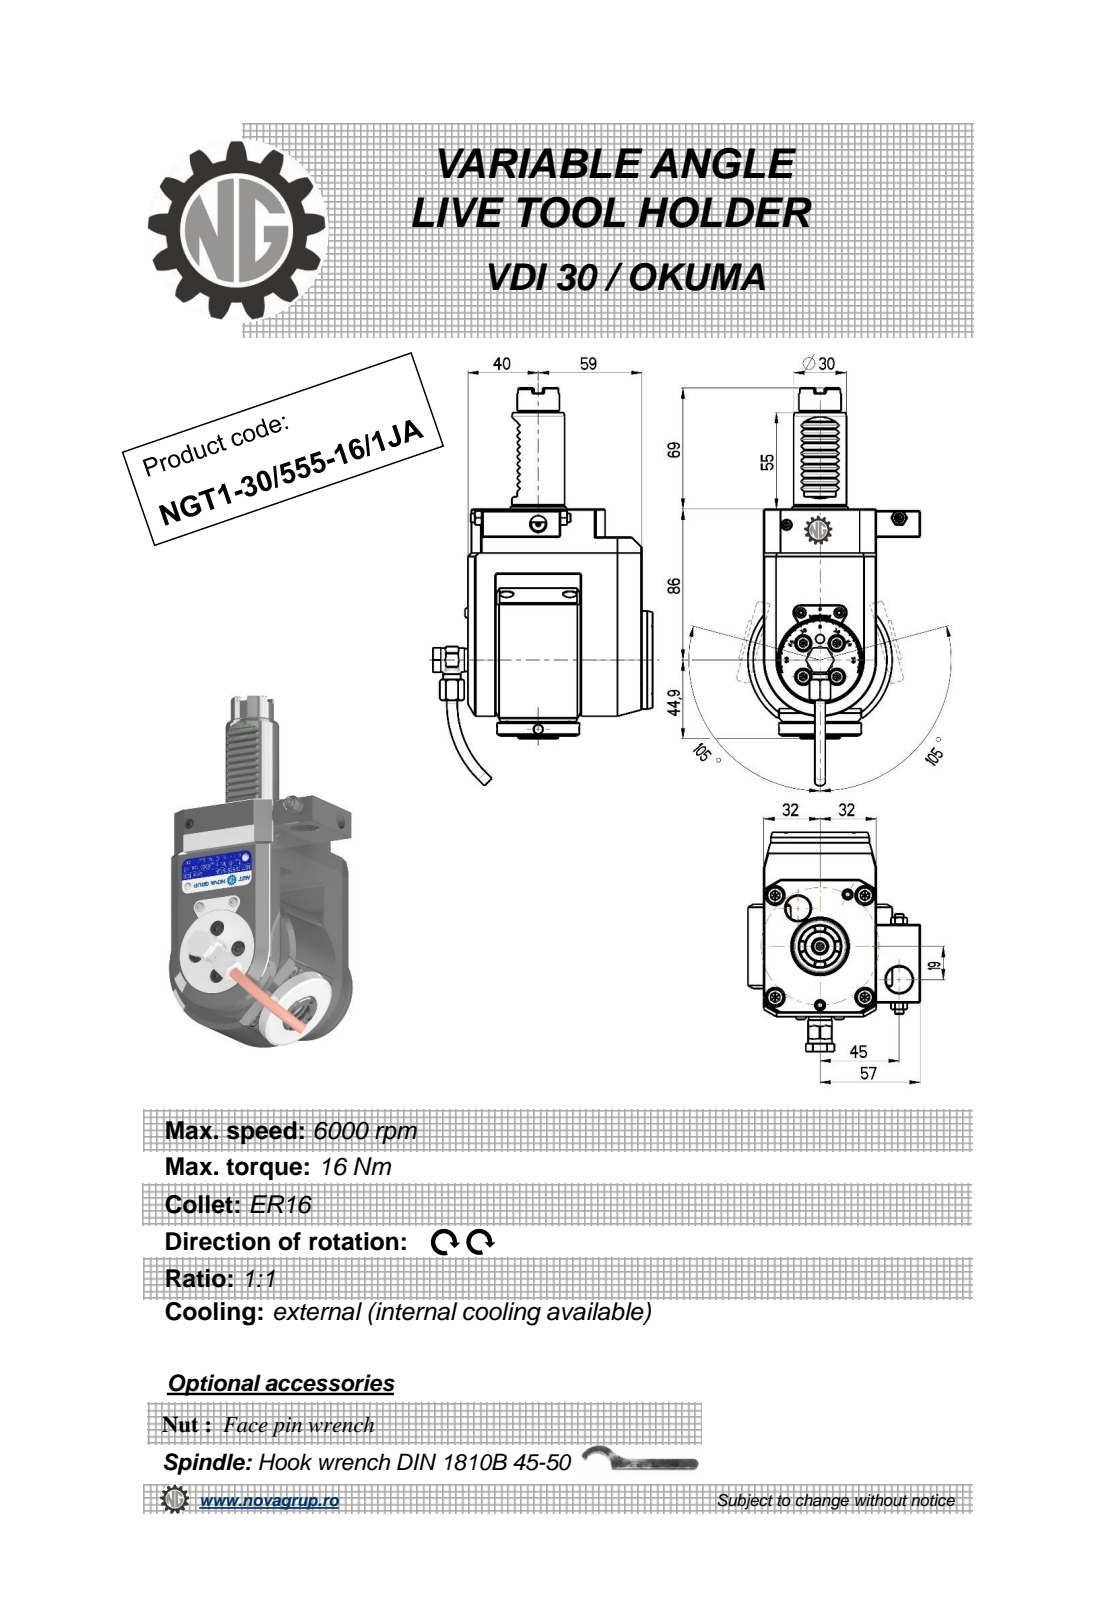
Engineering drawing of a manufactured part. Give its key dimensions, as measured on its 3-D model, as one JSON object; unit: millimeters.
{"part_name": "NGT1_30_555_16_1JA", "step_written_by": "PRO/ENGINEER BY PARAMETRIC TECHNOLOGY CORPORATION, 2010280 (CONFIG_CONTROL_DESIGN)", "units": "millimeters", "bodies": {"solids": 1, "faces": 568, "planar": 236, "cylindrical": 146, "other": 186}, "overall_size": [226.67, 124.9, 98], "volume_mm3": 771443, "surface_area_mm2": 75579, "round_holes": [[3.2, 4], [4, 3], [5, 2], [3, 1], [4.2, 1], [6, 1], [6.2, 1], [9, 1], [9.5, 1], [11, 1], [12.5, 1], [15, 1]], "round_bosses_or_shafts": [[10, 2], [6, 2], [5.7, 2], [82, 1], [56, 1], [47, 1], [36, 1], [30, 1]], "partial_cylinders_radius": [[0.26, 12], [0.3, 10], [0.16, 6], [0.5, 4], [1, 2], [7.7, 1], [32, 1]], "face_to_face_distances": [64, 16, 37, 6, 21, 89, 99, 105, 14, 41], "hole_center_spacings": [9.25, 13.08, 18.5, 49.87, 50.26, 0.4, 39.45, 39.75]}
